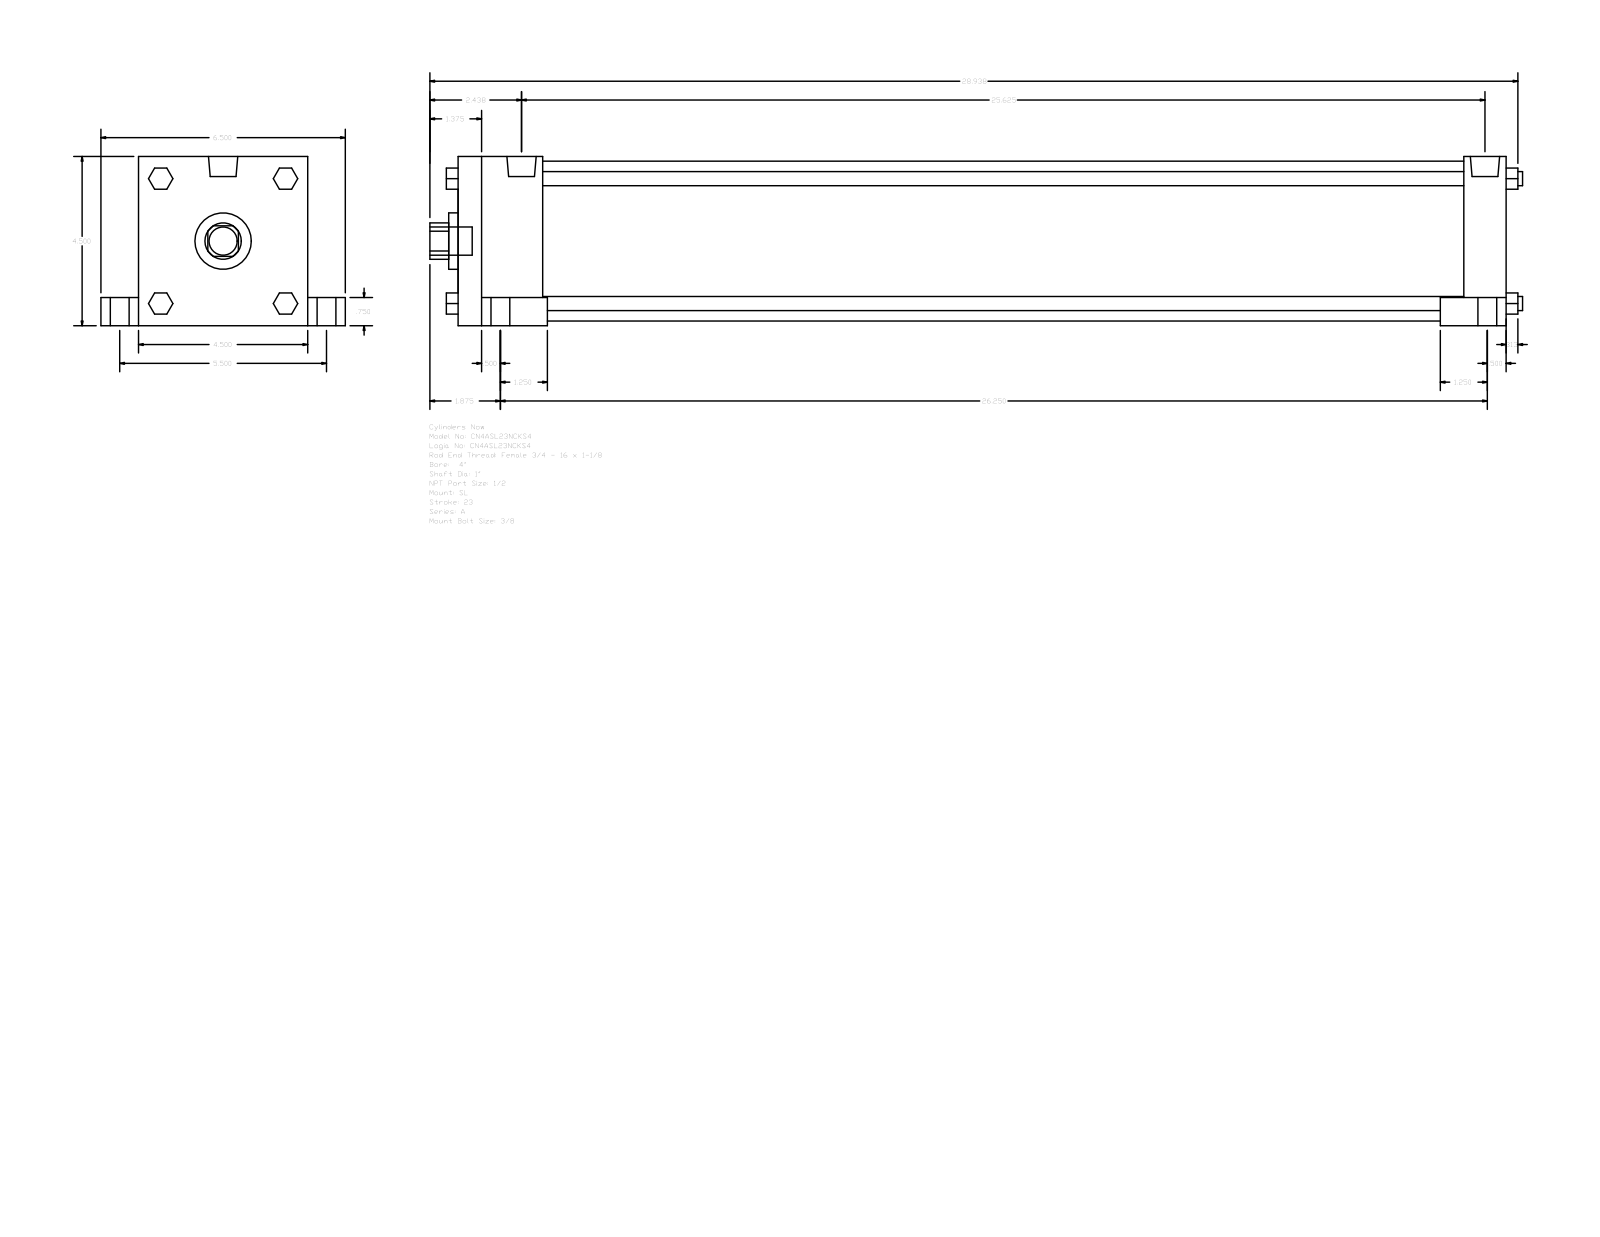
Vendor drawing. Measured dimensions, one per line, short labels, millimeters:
name: A_SL__0400_1
written by: GSSL Pune (CONFIG_CONTROL_DESIGN)
unit: mm
bodies: 0 solids, 150 faces (114 planar, 36 cylindrical, 0 other)
size: 738.19 × 165.1 × 114.3
holes: 1× ⌀25.4, 1× ⌀38.1, 1× ⌀107.95
bosses: 5× ⌀19.05, 4× ⌀12.7, 4× ⌀9.53, 4× ⌀8.73, 2× ⌀19.77
rounds: 1× R12.29
face distances: 114.3, 708.03, 57.15, 650.88, 679.45, 622.3, 28.58, 19.05, 25.4, 139.7
